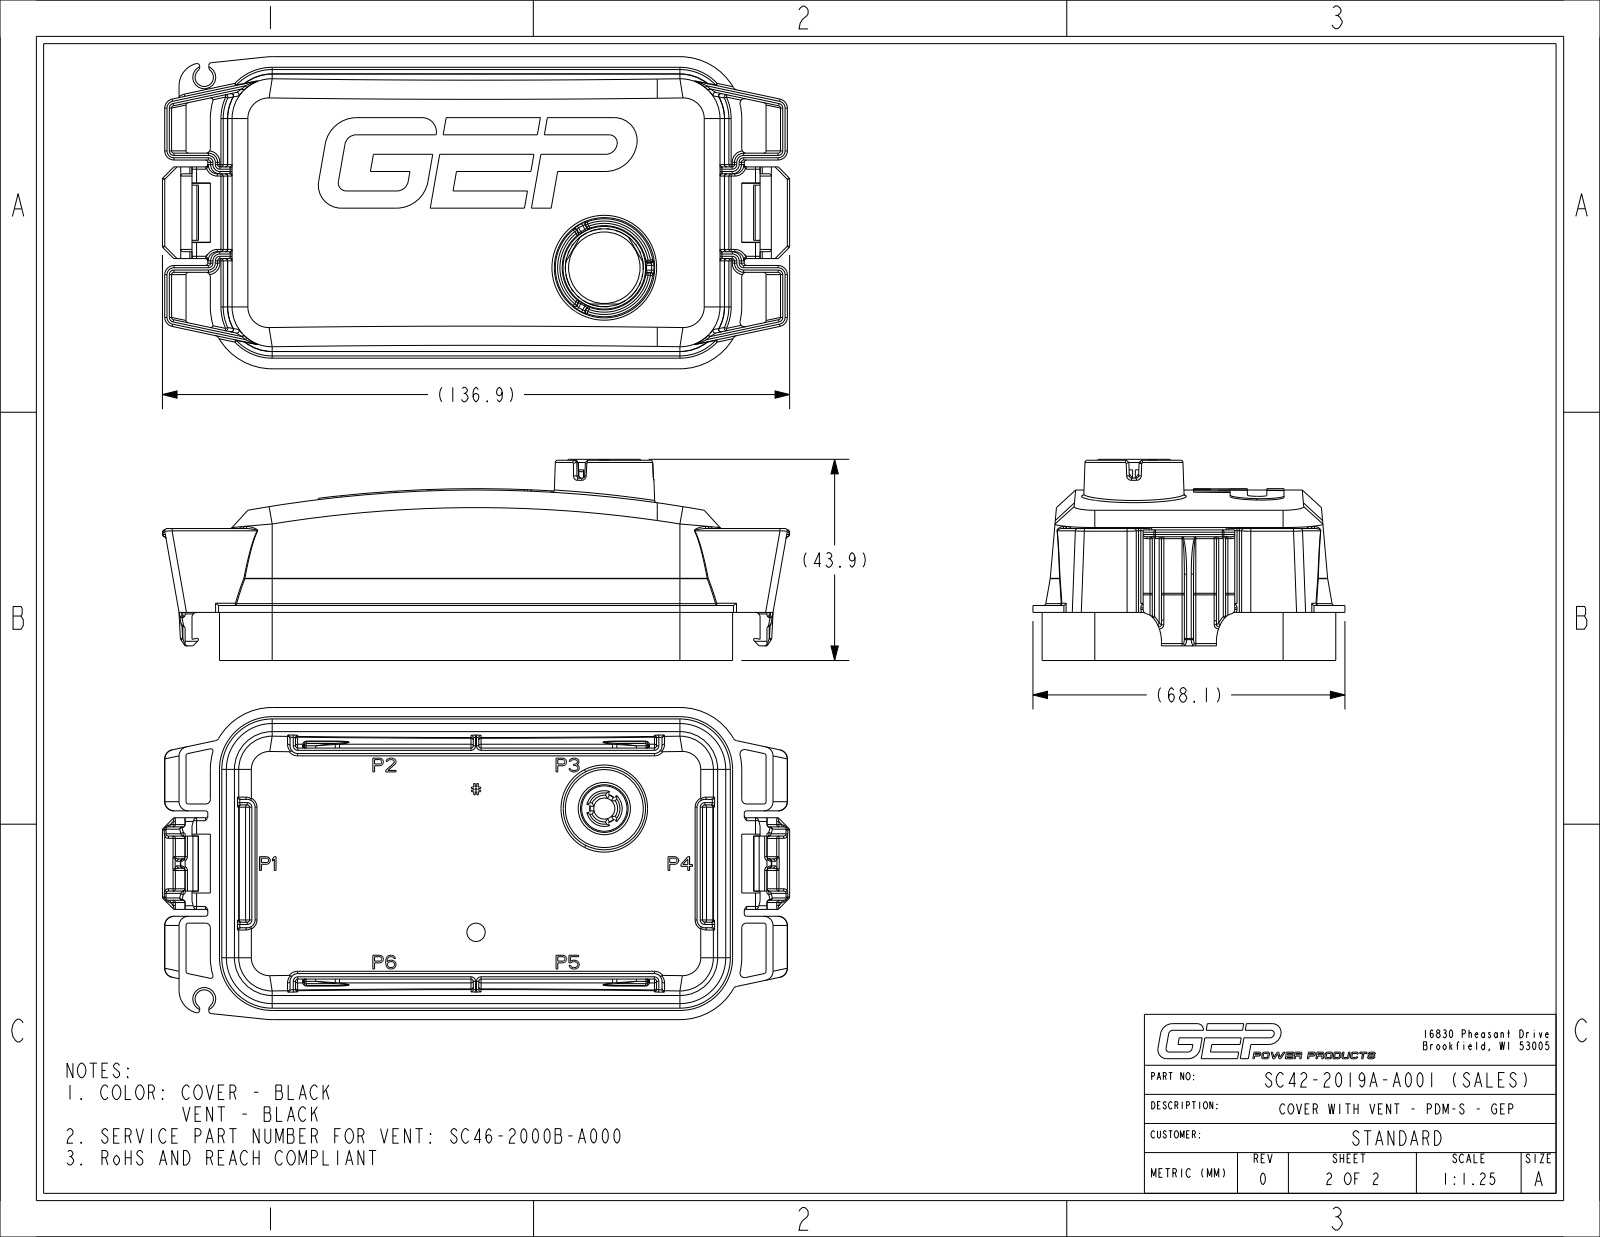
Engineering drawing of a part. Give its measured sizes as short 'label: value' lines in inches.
name: PC27-2000D-B001_NCF; PC46-2000B-A000_NCF; PC42-2019A-A001_NCF_ASM; SC42-2019A-A001_NCF_ASM
written by: CREO PARAMETRIC BY PTC INC, 2017110 (CONFIG_CONTROL_DESIGN)
unit: in
bodies: 3 solids, 1734 faces (501 planar, 467 cylindrical, 766 other)
size: 5.39 × 2.681 × 1.728
volume: 2.211 in³; area: 74.6 in²
holes: 1× ⌀0.157, 1× ⌀0.181, 1× ⌀0.252, 1× ⌀0.378
bosses: 1× ⌀0.669, 1× ⌀0.409, 1× ⌀0.244
rounds: 234× R0.02, 22× R0.079, 19× R0.039, 8× R0.067, 4× R0.016, 4× R0.02, 4× R0.024, 4× R0.394
face distances: 0.059, 2.465, 0.317, 2.207, 0.258, 2.148, 0.047, 0.079, 2.524, 0.27
hole spacings: 3.807
